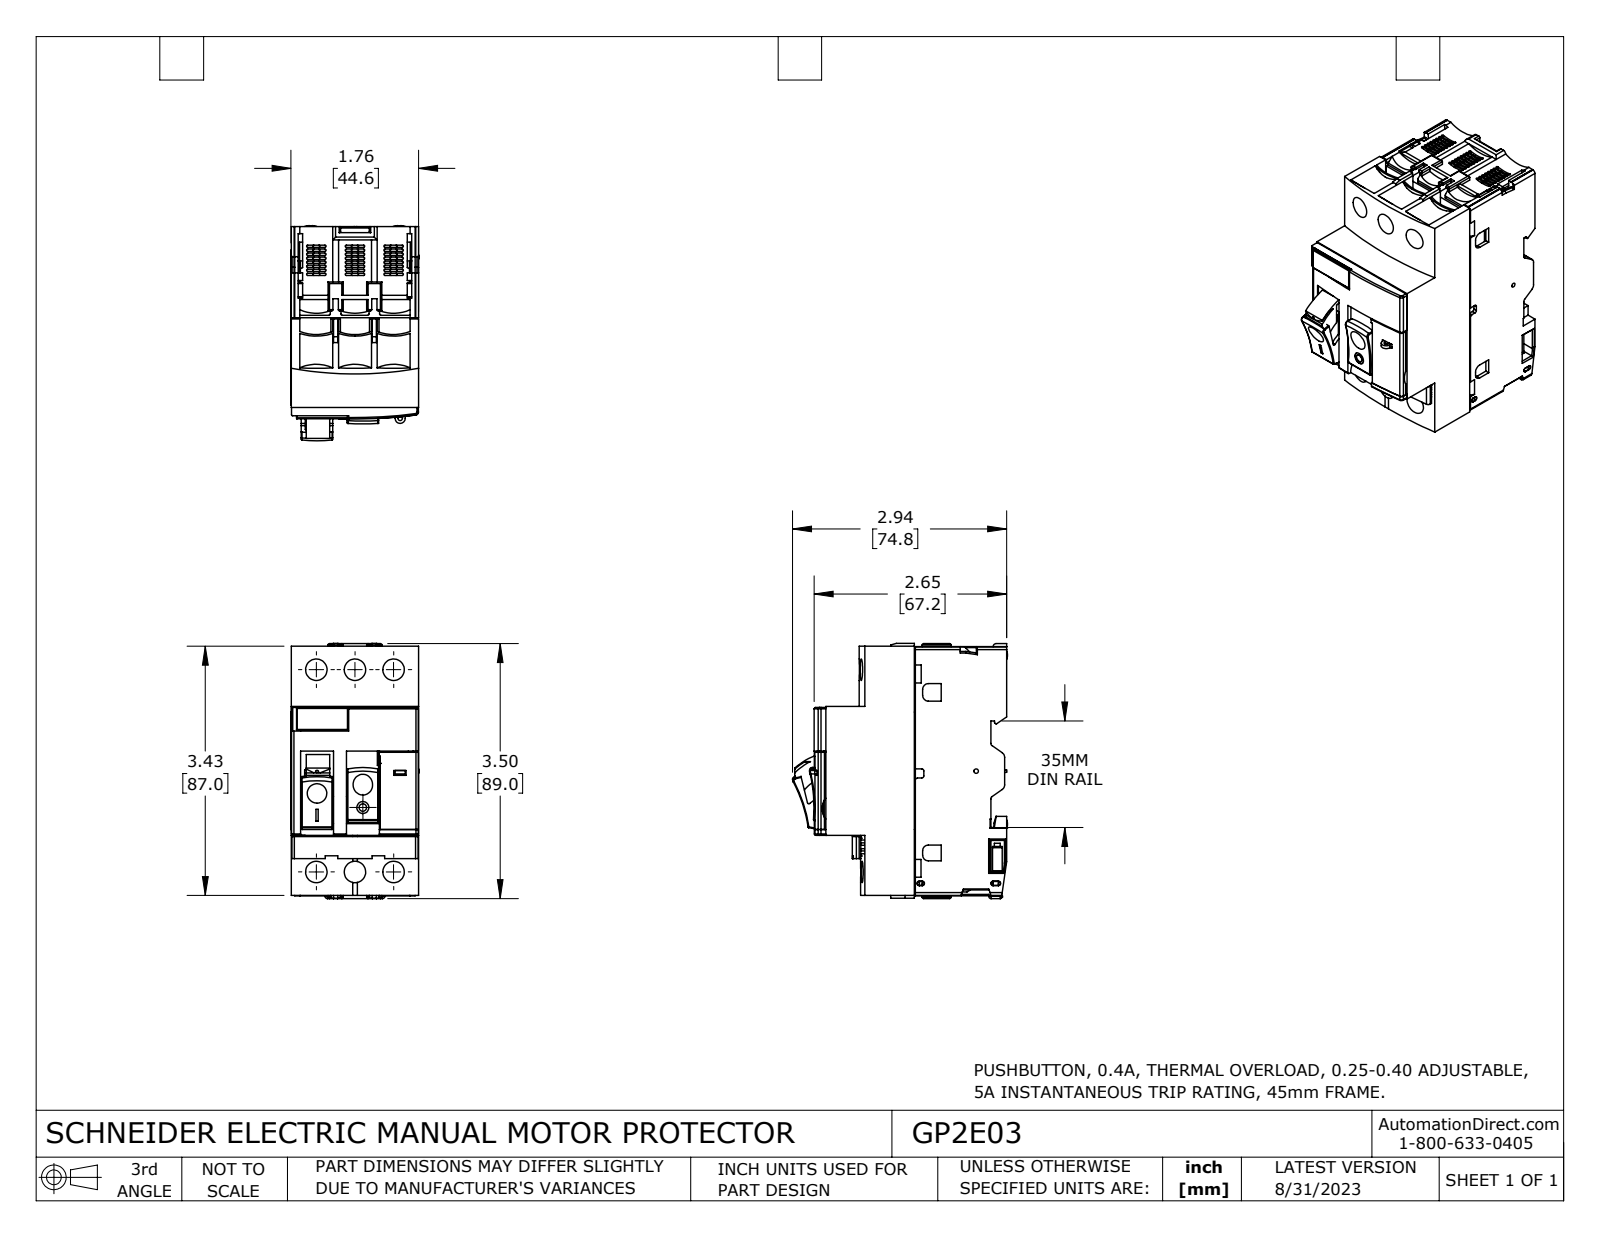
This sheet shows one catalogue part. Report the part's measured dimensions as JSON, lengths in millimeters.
{"part_name": "GP2E03", "step_written_by": "SolidWorks 2021 (CONFIG_CONTROL_DESIGN)", "units": "millimeters", "bodies": {"solids": 15, "faces": 2269, "planar": 1521, "cylindrical": 657, "other": 91}, "overall_size": [89.1, 75.1, 44.8], "volume_mm3": 189800, "surface_area_mm2": 63830, "round_holes": [[7.5, 6], [5, 5], [1.5, 2], [4, 1], [4.2, 1], [8, 1], [8.3, 1], [8.5, 1], [8.7, 1]], "round_bosses_or_shafts": [[6.2, 2], [3, 2], [9.7, 1], [2.6, 1], [1.2, 1]], "partial_cylinders_radius": [[0.4, 104], [0.5, 47], [1, 16], [0.3, 12], [0.3, 12], [0.8, 12], [1.5, 8], [0.1, 6]], "face_to_face_distances": [44.5, 13.5, 2.9, 31.3, 44.6, 1.5, 41.6, 14.8, 26.7, 29.7], "hole_center_spacings": [13.5, 71.9, 70.6, 8.8, 10.2, 13.9, 17, 18.4]}
